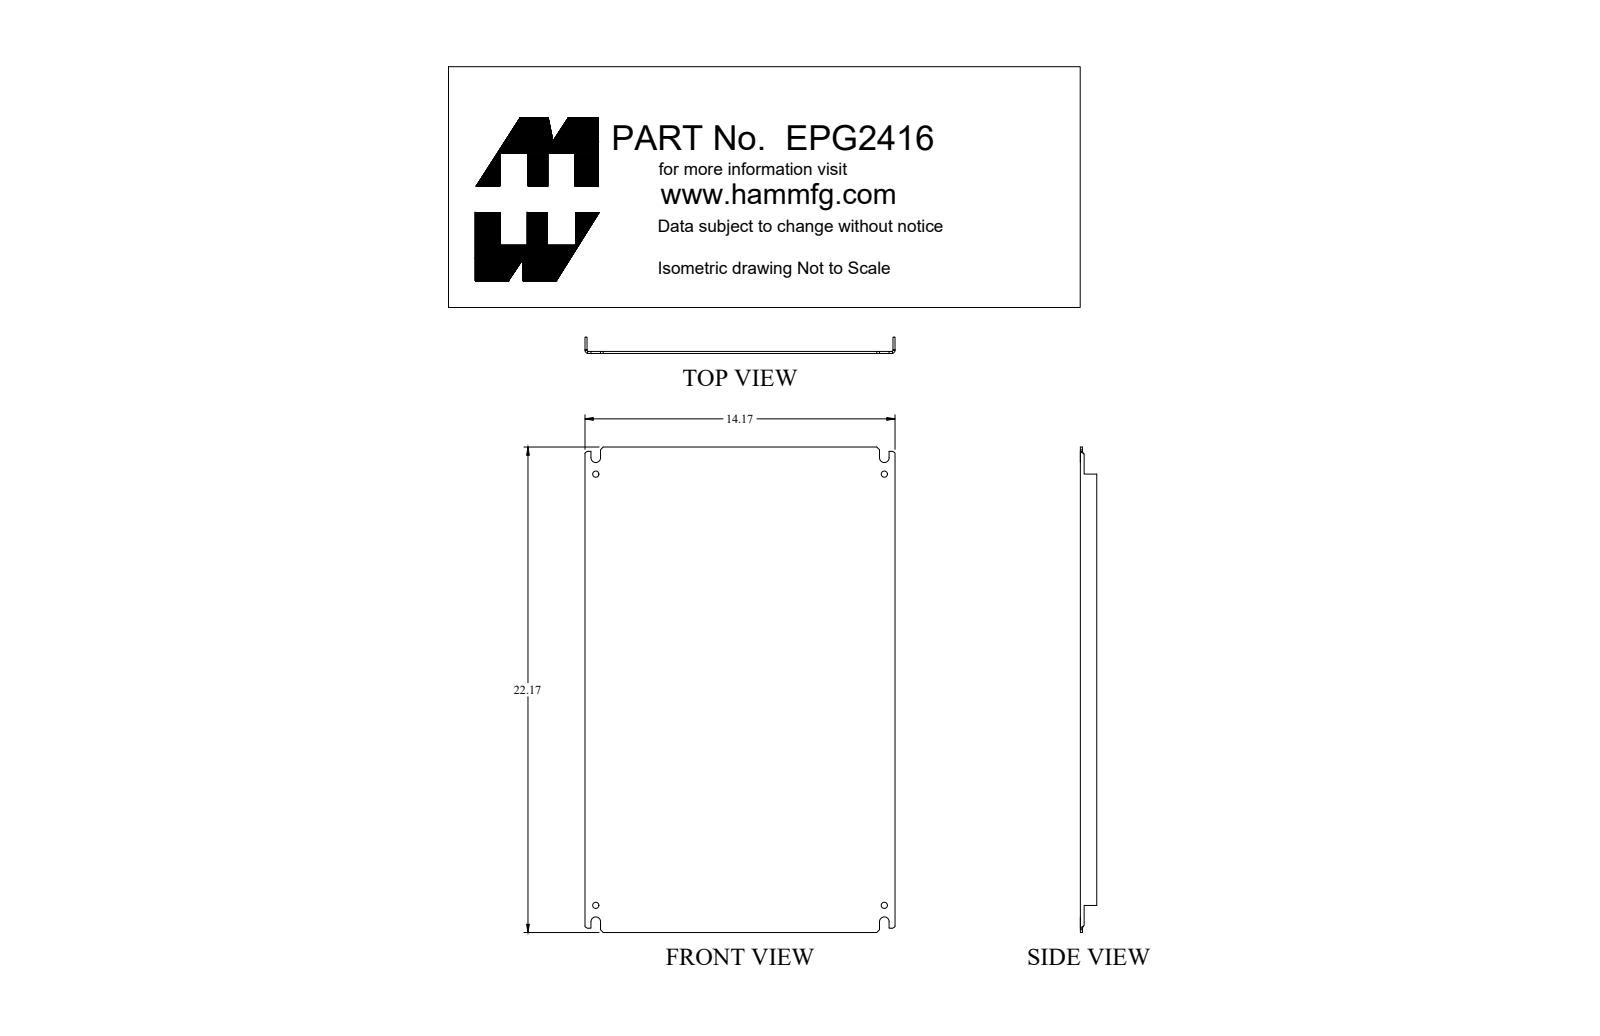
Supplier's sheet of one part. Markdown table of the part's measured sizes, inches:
| quantity | value |
| --- | --- |
| part name | EPG2416 |
| STEP written by | SolidWorks 2018 (AUTOMOTIVE_DESIGN) |
| units | inches |
| bodies | 1 solid, 84 faces (50 planar, 26 cylindrical, 8 other) |
| overall size | 22.17 × 14.17 × 0.75 |
| volume | 31.99 in³ |
| surface area | 681.2 in² |
| round holes (diameter × count) | 0.281 × 4 |
| partial cylindrical surfaces (radius × count) | 0.219 × 4, 0.048 × 2, 0.062 × 2, 0.143 × 2 |
| main face-to-face distances | 0.095, 14.075, 13.98, 14.17, 0.75, 0.655, 22.17, 0.171, 0.076, 0.579 |
| hole center spacings | 13.188, 19.688, 23.697 |
